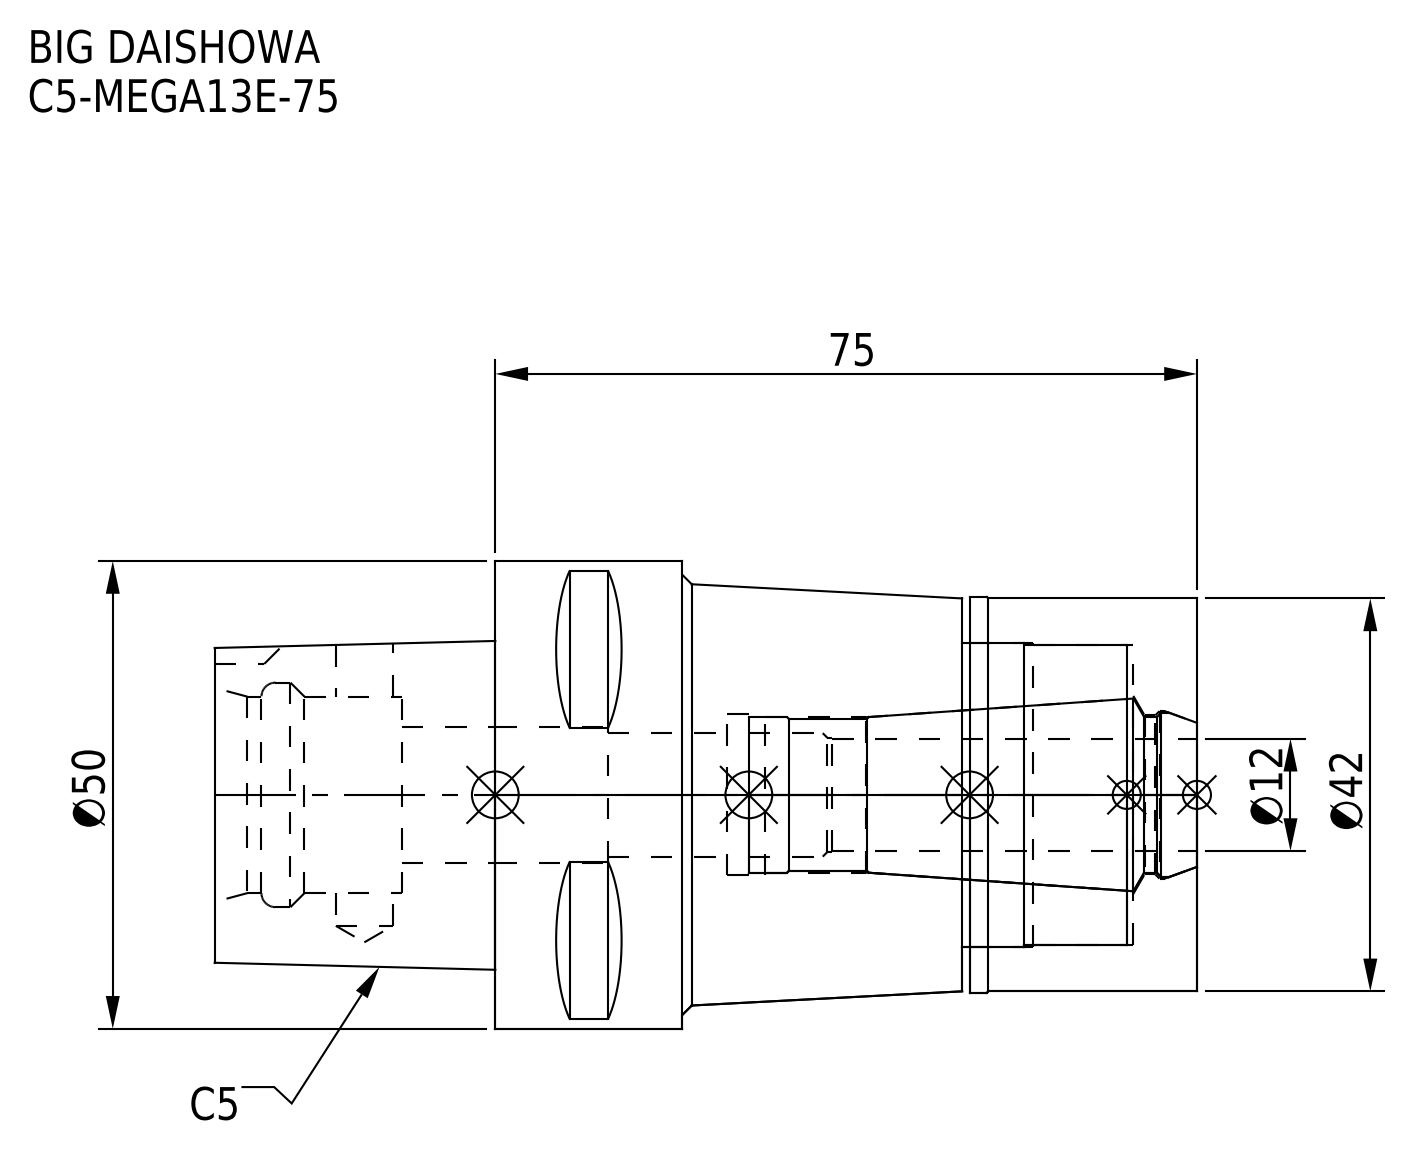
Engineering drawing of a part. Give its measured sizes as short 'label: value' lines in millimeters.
name: C5-MEGA13E-75; C5-MEGA13E-75_1.stp; C5-MEGA13E-75-120.stp; C5-MEGA13E-75-120_ASM.stp (+3 more)
written by: SolidWorks 2019 (CONFIG_CONTROL_DESIGN)
unit: mm
bodies: 2 solids, 97 faces (36 planar, 37 cylindrical, 24 other)
size: 105 × 50 × 50
volume: 118 716 mm³; area: 28 847 mm²
holes: 1× ⌀6.1, 1× ⌀13.3, 1× ⌀14.5, 1× ⌀16.6, 1× ⌀17, 1× ⌀17.2, 1× ⌀17.9, 1× ⌀21, 1× ⌀24, 1× ⌀32, 1× ⌀32.5
bosses: 1× ⌀50, 1× ⌀42.3, 1× ⌀42
rounds: 1× R4
face distances: 75, 25.1, 24.3, 50.7, 30, 0.8, 49.9, 67.5, 16.8, 6.8
